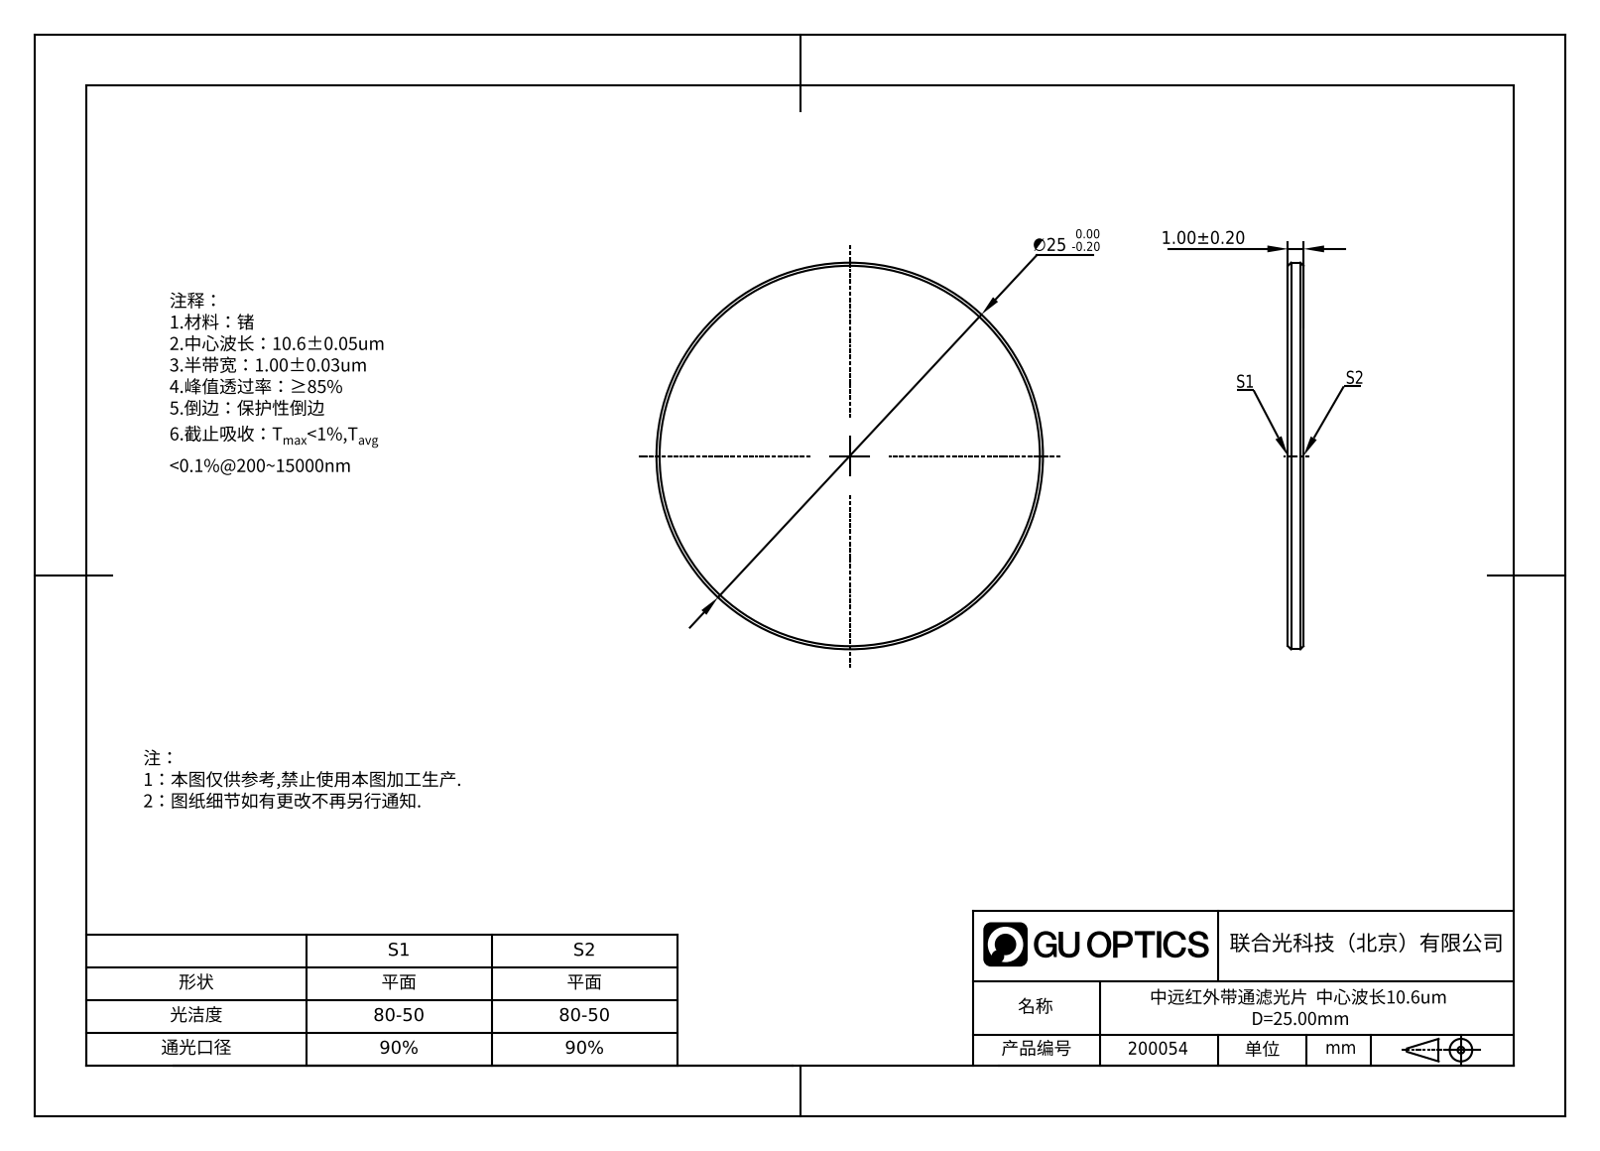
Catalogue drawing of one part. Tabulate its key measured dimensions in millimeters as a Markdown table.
| quantity | value |
| --- | --- |
| part name | GNIF-1000-10600-D25 |
| STEP written by | SolidWorks 2022 (AUTOMOTIVE_DESIGN) |
| units | millimeters |
| bodies | 1 solid, 8 faces (2 planar, 2 cylindrical, 4 other) |
| overall size | 25 × 25 × 1 |
| volume | 488 mm³ |
| surface area | 1 042 mm² |
| round bosses / shafts (diameter × count) | 25 × 1 |
| main face-to-face distances | 1 |
